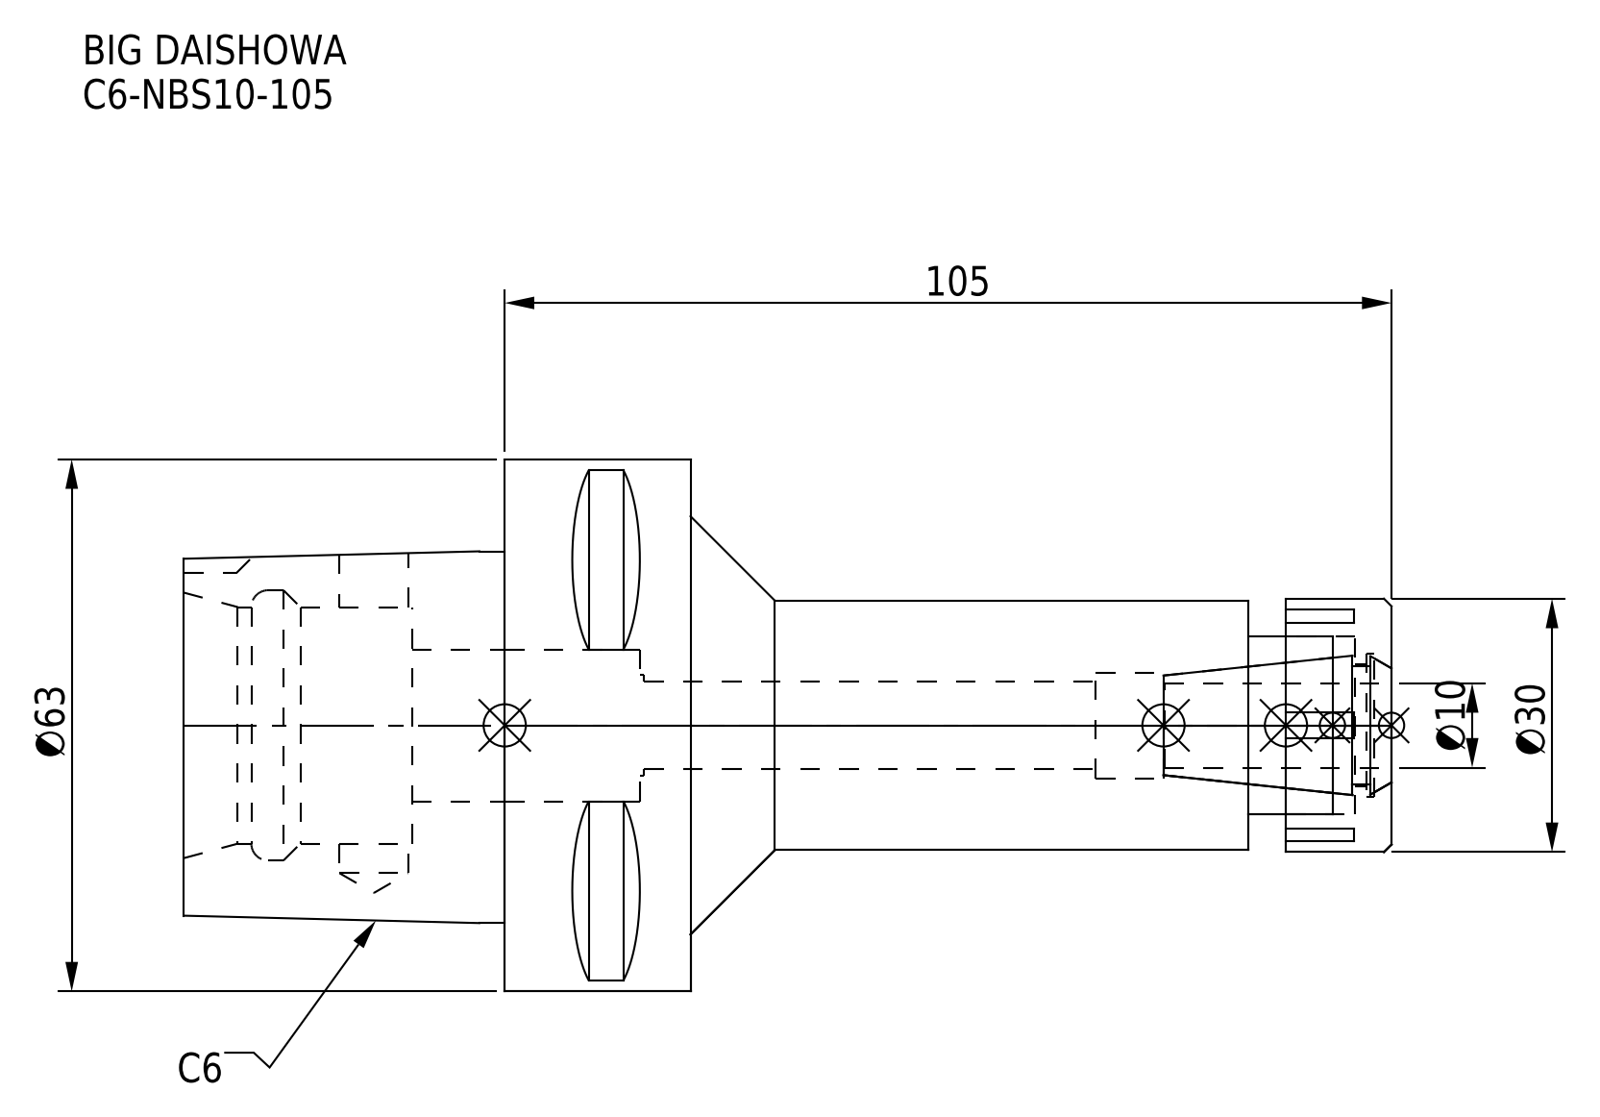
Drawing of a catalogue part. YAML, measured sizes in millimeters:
part_name: "C6-NBS10-105-100_ASM.stp; C6-NBS10-105; C6-NBS10-105.stp; DXF_TEMP_ASSY_ASM_4_ASM.stp (+3 more)"
step_written_by: "SolidWorks 2019 (CONFIG_CONTROL_DESIGN)"
units: millimeters
bodies: {solids: 2, faces: 112, planar: 61, cylindrical: 33, other: 18}
overall_size: [143, 63, 63]
volume: 147094
surface_area: 32499
round_holes:
  - {diameter: 8.1, count: 1}
  - {diameter: 10.4, count: 1}
  - {diameter: 12, count: 1}
  - {diameter: 12.5, count: 1}
  - {diameter: 14.5, count: 1}
  - {diameter: 17, count: 1}
  - {diameter: 18, count: 1}
  - {diameter: 21, count: 1}
  - {diameter: 28, count: 1}
  - {diameter: 32, count: 1}
round_bosses_or_shafts:
  - {diameter: 63, count: 1}
  - {diameter: 30, count: 1}
  - {diameter: 29.5, count: 1}
partial_cylinders:
  - {radius: 5, count: 1}
face_to_face_distances: [22, 27, 60, 38, 83, 105, 143, 33, 116, 11]
